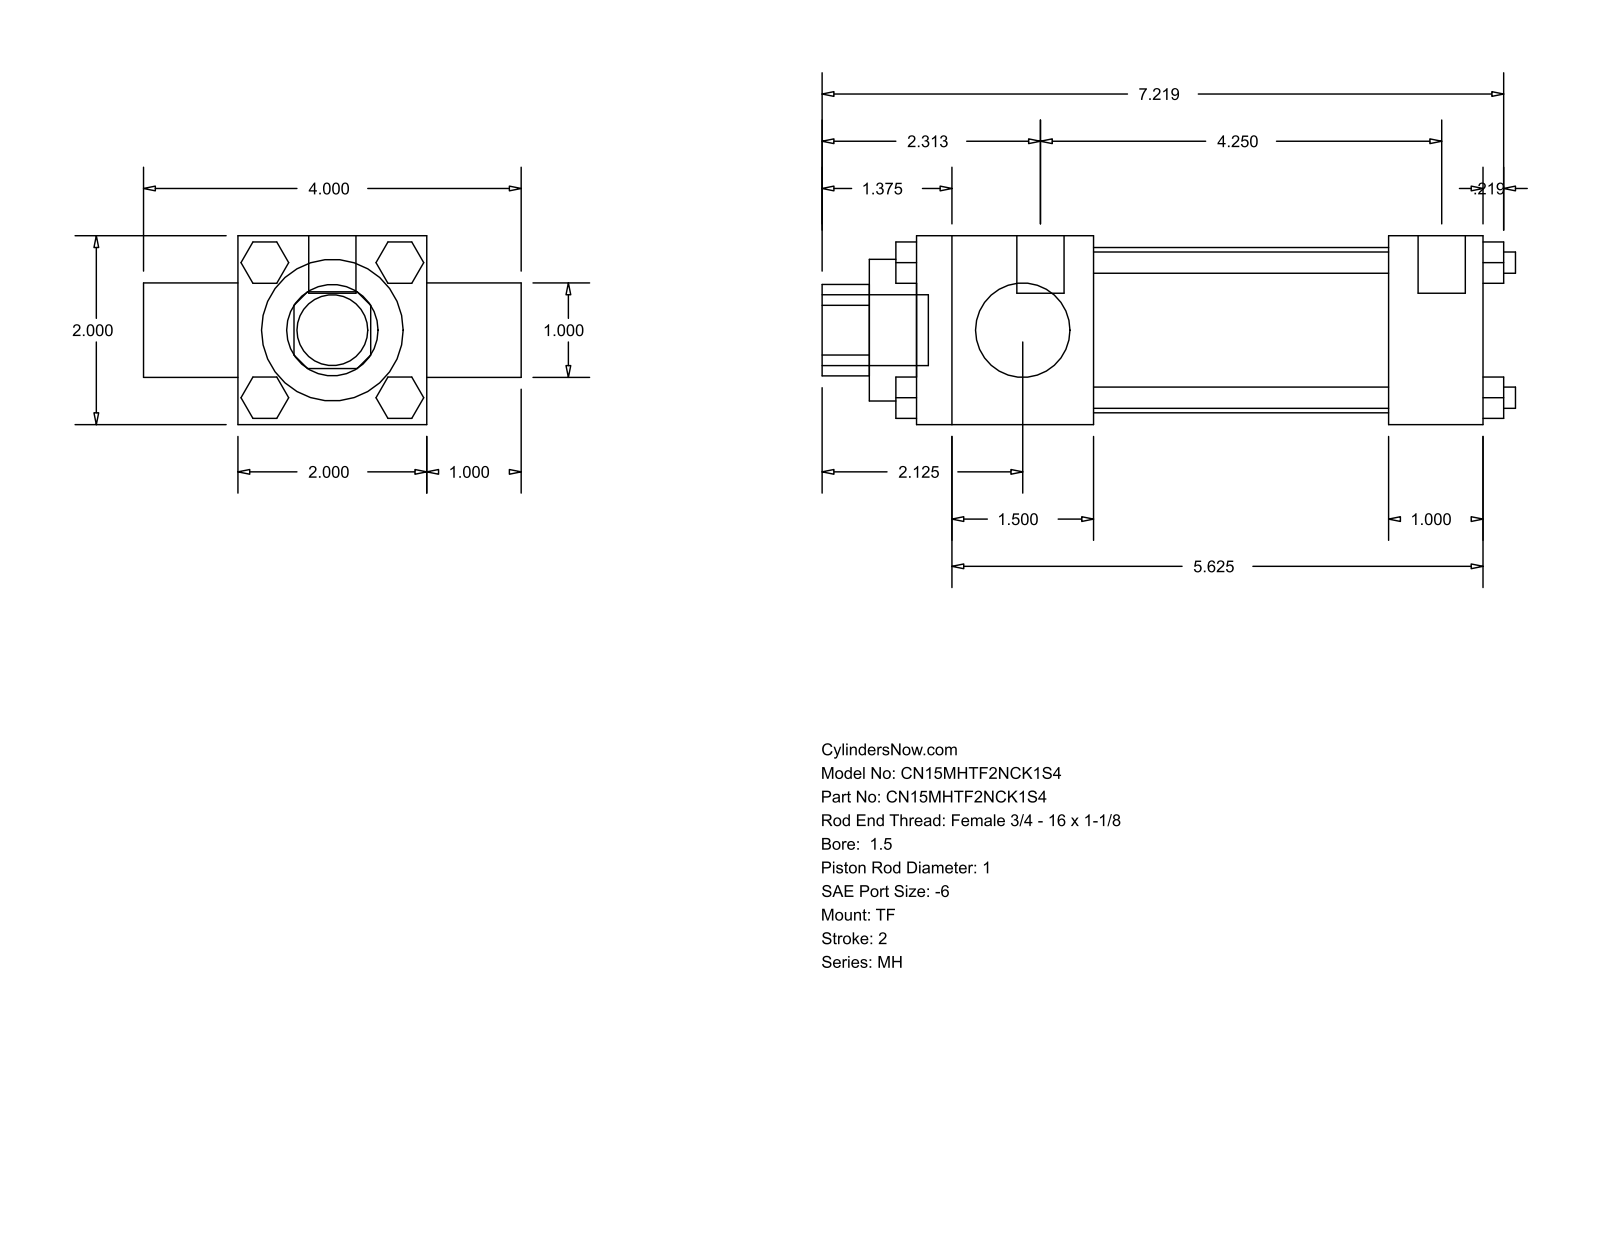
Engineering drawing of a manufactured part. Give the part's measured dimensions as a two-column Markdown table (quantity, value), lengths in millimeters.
| quantity | value |
| --- | --- |
| part name | MH_TF__0150_1 |
| STEP written by | GSSL Pune (CONFIG_CONTROL_DESIGN) |
| units | millimeters |
| bodies | 0 solids, 120 faces (92 planar, 28 cylindrical, 0 other) |
| overall size | 186.53 × 101.6 × 50.8 |
| round holes (diameter × count) | 25.4 × 2, 38.1 × 1, 44.45 × 1 |
| round bosses / shafts (diameter × count) | 5.71 × 4, 5.56 × 3, 12.7 × 2, 19.05 × 1 |
| partial cylindrical surfaces (radius × count) | 12.29 × 1 |
| main face-to-face distances | 50.8, 25.4, 152.4, 76.2, 47.63, 104.77, 127, 79.37, 157.96, 12.7 |
